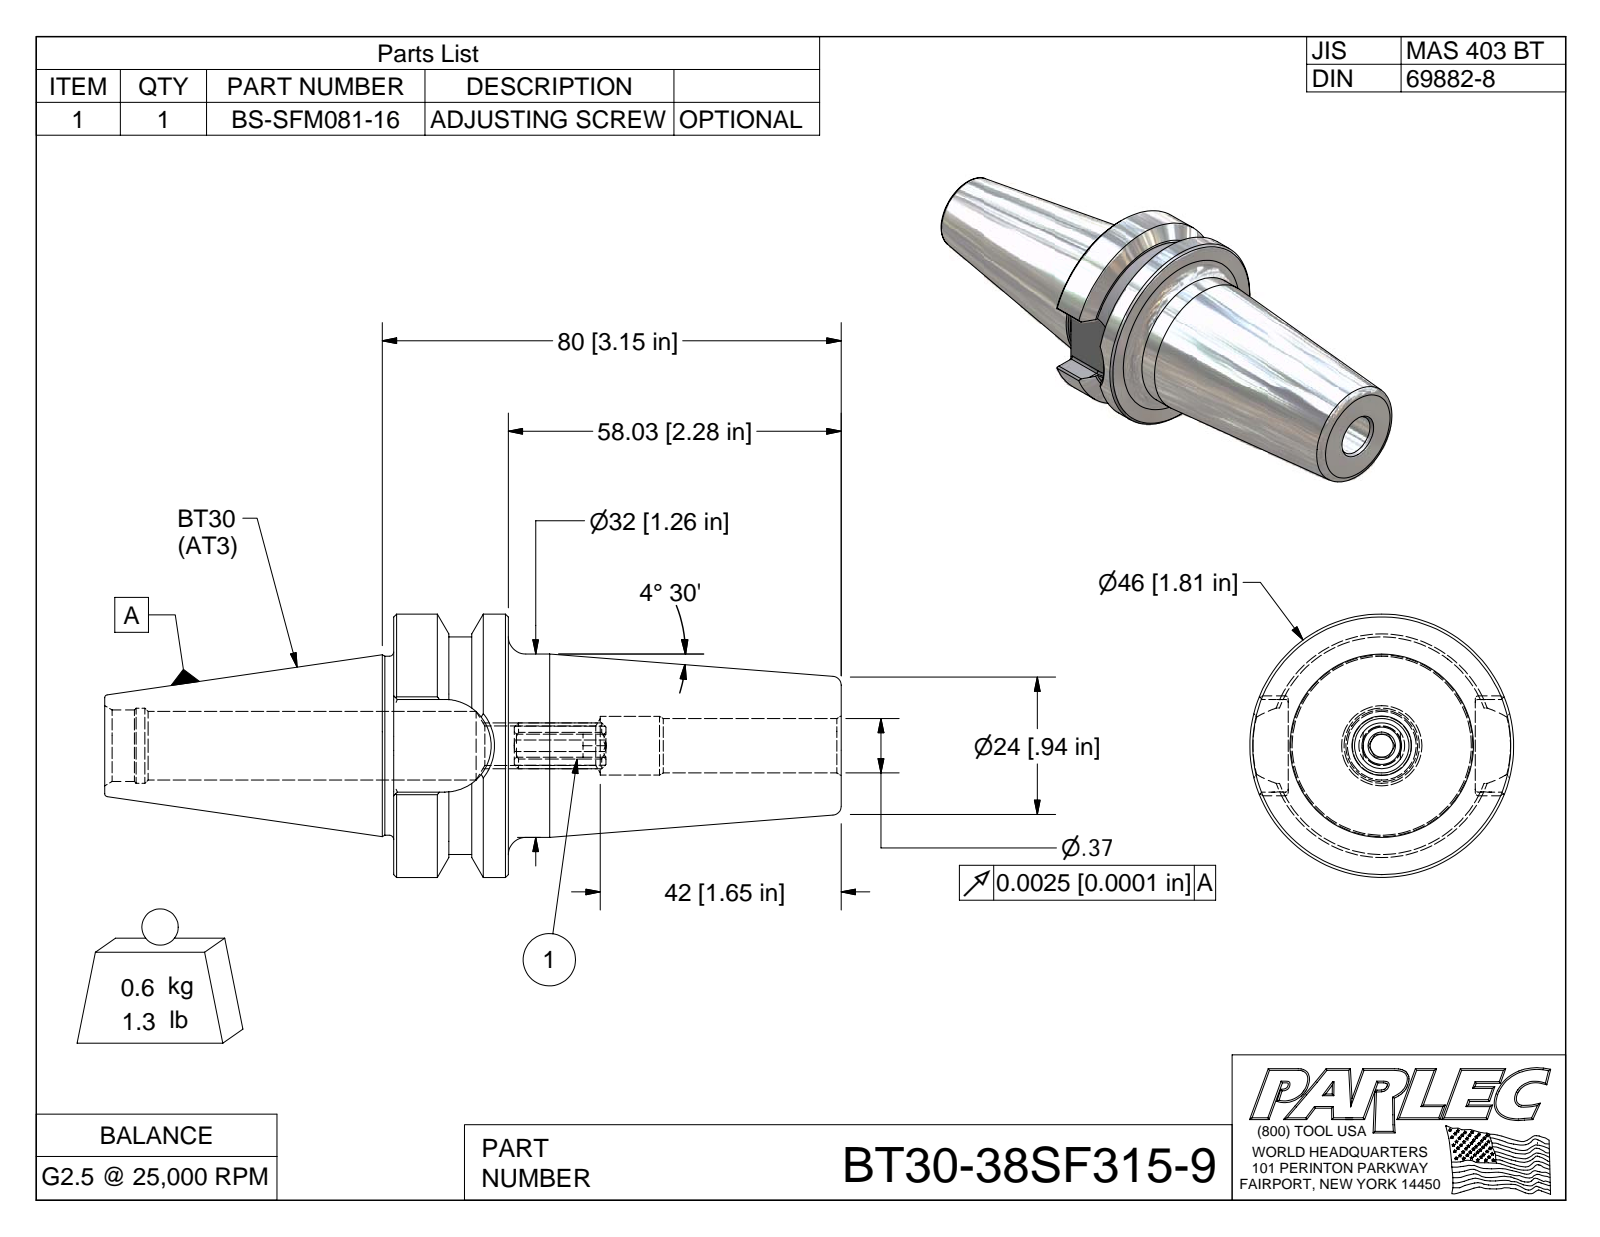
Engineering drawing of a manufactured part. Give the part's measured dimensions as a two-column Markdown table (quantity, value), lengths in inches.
| quantity | value |
| --- | --- |
| part name | BT30-38SF315-9; BT30-38SF315-9-1; BS-SFM081-16 |
| STEP written by | Autodesk Inventor 2009 (AUTOMOTIVE_DESIGN) |
| units | inches |
| bodies | 2 solids, 92 faces (35 planar, 22 cylindrical, 35 other) |
| overall size | 5.056 × 1.811 × 1.811 |
| volume | 4.859 in³ |
| surface area | 30.2 in² |
| round holes (diameter × count) | 0.374 × 1, 0.404 × 1, 0.517 × 1 |
| round bosses / shafts (diameter × count) | 1.811 × 1, 1.26 × 1, 1.23 × 1 |
| partial cylindrical surfaces (radius × count) | 0.02 × 8, 0.157 × 1, 0.319 × 1, 0.748 × 1 |
| main face-to-face distances | 0.787, 3.072, 2.285, 1.283, 0.514, 0.77, 0.157, 0.256, 1.984, 2.771 |
